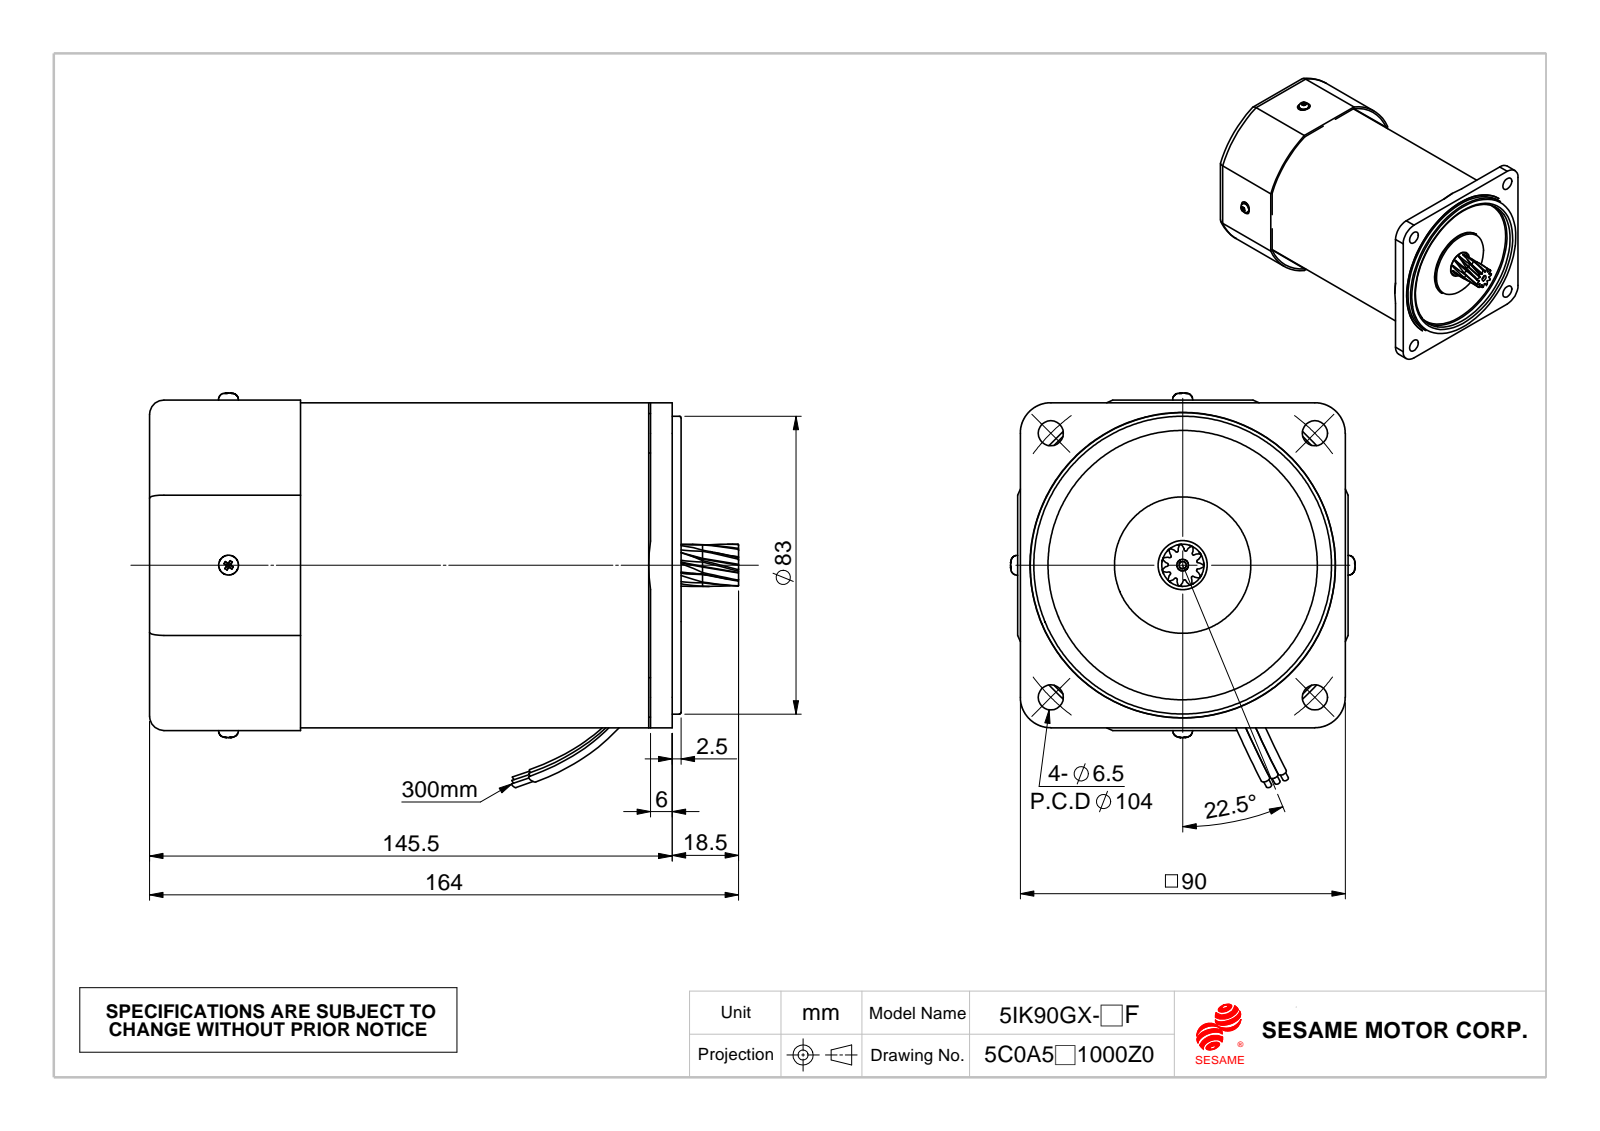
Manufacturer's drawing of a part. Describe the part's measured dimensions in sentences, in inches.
The part is named "90GX_1成品; 線扣; M590-F; 風扇蓋FC-9042-21". Its 3-D file was written by "SolidWorks 2010 (CONFIG_CONTROL_DESIGN)". It is 12 solids with 594 faces: 196 planar, 210 cylindrical and 188 other. Overall it measures 6.457 by 4.326 by 3.776 inches. Its volume is 53.19 cubic inches and its surface area 174.6 square inches. Round holes: 4 of diameter 0.276, 3 of diameter 0.098, 1 of diameter 0.079, 1 of diameter 0.256, 1 of diameter 0.283, 1 of diameter 0.374, 1 of diameter 0.539, 1 of diameter 0.945, 1 of diameter 1.024, 1 of diameter 1.575, 1 of diameter 2.126, 1 of diameter 2.287. Round bosses or shafts: 3 of diameter 0.433, 2 of diameter 0.217, 2 of diameter 0.118, 1 of diameter 3.563, 1 of diameter 3.386, 1 of diameter 3.313, 1 of diameter 3.307, 1 of diameter 3.265. Partial cylindrical surfaces (rounded edges, fillets, slot ends): 16 of radius 0.012, 8 of radius 0.01, 8 of radius 0.039, 4 of radius 0.069, 4 of radius 0.079, 4 of radius 0.089, 4 of radius 0.118, 4 of radius 0.157. The main face-to-face distances are 0.039, 3.583, 0.63, 5.472, 5.626, 5.665, 5.512, 0.154, 5.669, 0.157. The hole center spacings are 2.047, 2.895, 4.094, 4.864.
